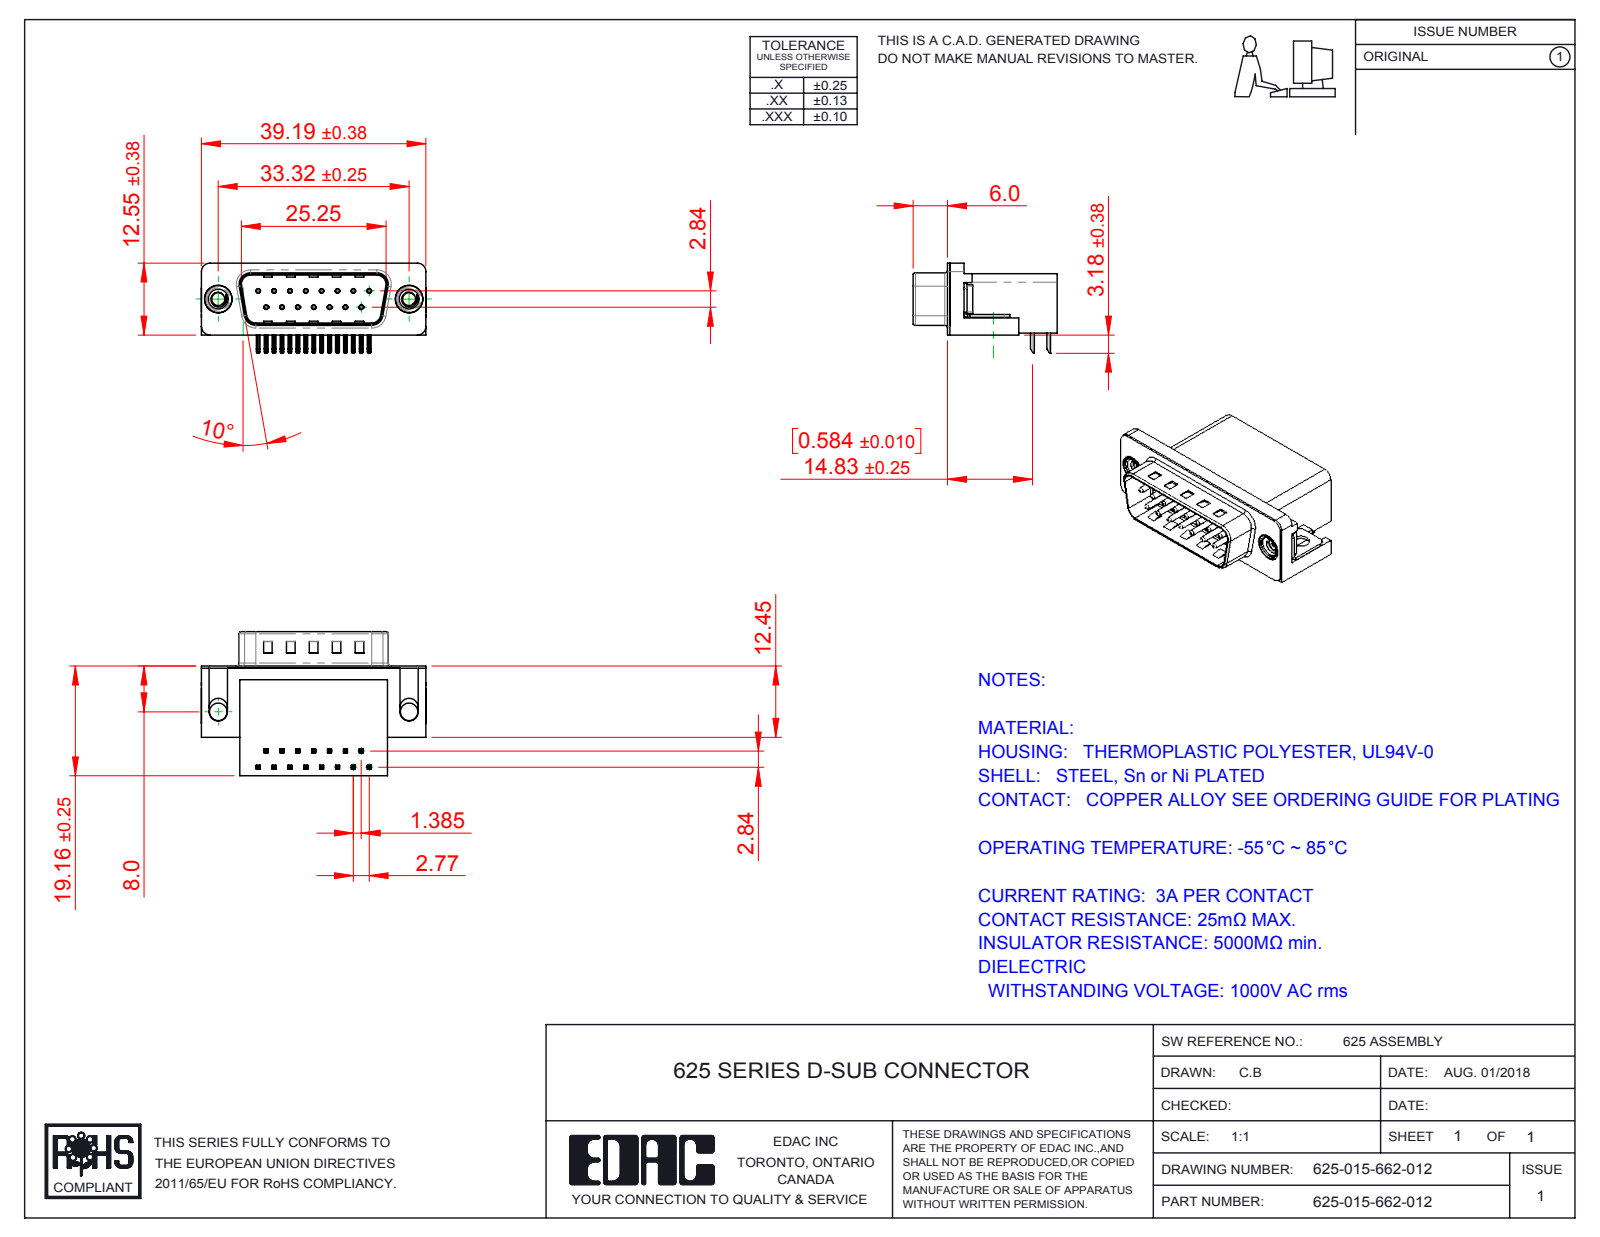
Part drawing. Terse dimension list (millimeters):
name: 625 Shell_15 Socket; 625 Thru Hole Board Mount; 625 Housing_15 Socket; 625 Contact Bottom (+3 more)
written by: SolidWorks 2016 (CONFIG_CONTROL_DESIGN)
unit: mm
bodies: 21 solids, 1479 faces (893 planar, 447 cylindrical, 139 other)
size: 39.22 × 25.16 × 15.73
volume: 6 242 mm³; area: 6 412 mm²
holes: 15× ⌀0.35, 15× ⌀0.8, 2× ⌀2.26, 2× ⌀3.05, 2× ⌀4, 2× ⌀4.8, 2× ⌀5
bosses: 15× ⌀0.75, 2× ⌀4.9, 2× ⌀4.75, 2× ⌀3.9
rounds: 68× R0.25, 30× R0.12, 16× R1, 9× R0.5, 8× R1.6, 6× R1.5, 4× R0.9, 4× R2
face distances: 0.4, 10.35, 18.76, 2.1, 10.46, 19.16, 1.7, 10.86, 8.76, 16.26
hole spacings: 3.16, 2.77, 5.54, 8.31, 11.08, 5.03, 5.04, 7.48
